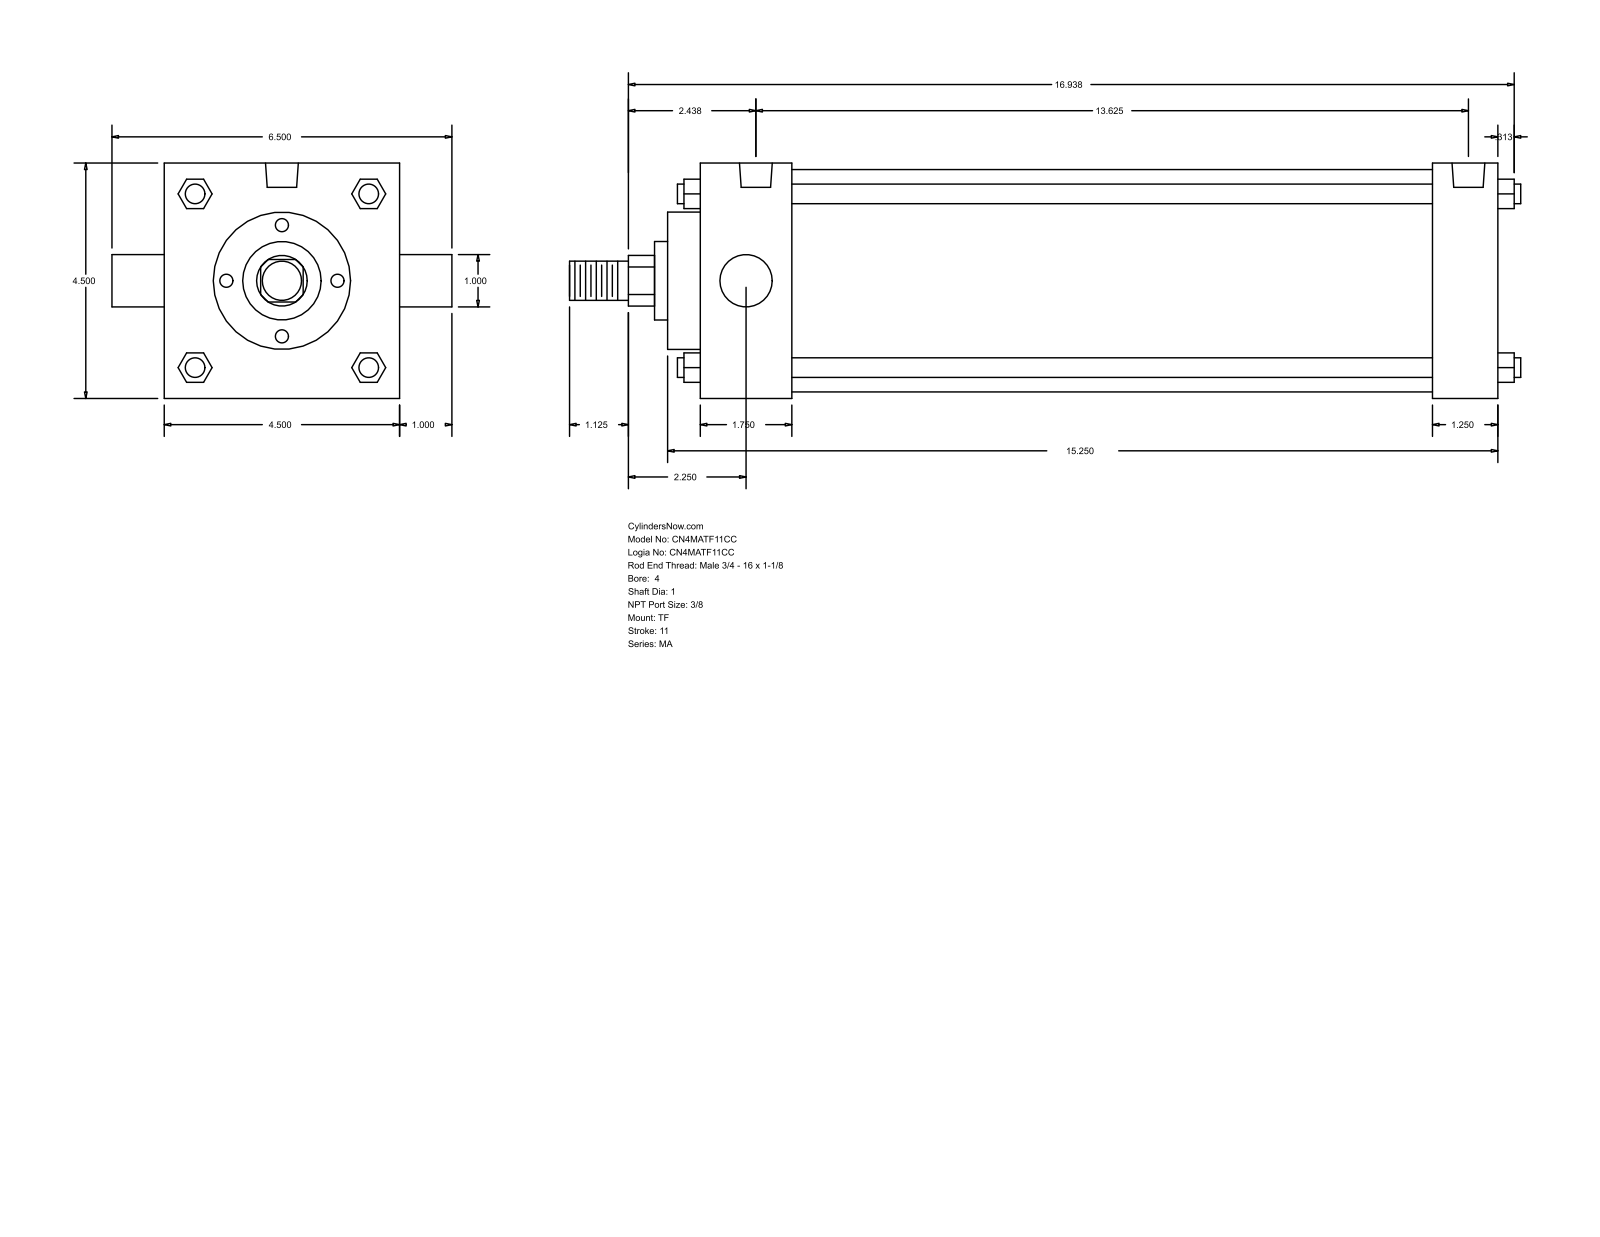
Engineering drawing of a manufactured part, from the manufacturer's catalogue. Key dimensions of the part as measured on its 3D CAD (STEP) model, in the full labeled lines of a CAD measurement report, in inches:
Part name (STEP PRODUCT): MA_TF__0400_1
STEP written by: GSSL Pune (CONFIG_CONTROL_DESIGN)
Units: inches
Bodies: 0 solids, 122 faces (93 planar, 29 cylindrical, 0 other)
Overall size (bounding box): 18.187 × 6.5 × 4.5
Round holes (diameter × count): ⌀0.437 ×3, ⌀0.627 ×2
Round bosses / shafts (diameter × count): ⌀0.375 ×4, ⌀1 ×2, ⌀4.25 ×1, ⌀2.625 ×1, ⌀1.5 ×1, ⌀0.75 ×1
Partial cylindrical surfaces — rounded edges, fillets, slot ends (radius × count): R0.484 ×1
Main face-to-face distances: 4.5, 15.25, 14, 1.25, 1.75, 12.25, 13.5, 15.875, 0.625, 2.375
Hole centre spacings: 0.187, 13.438, 13.25, 13.625
